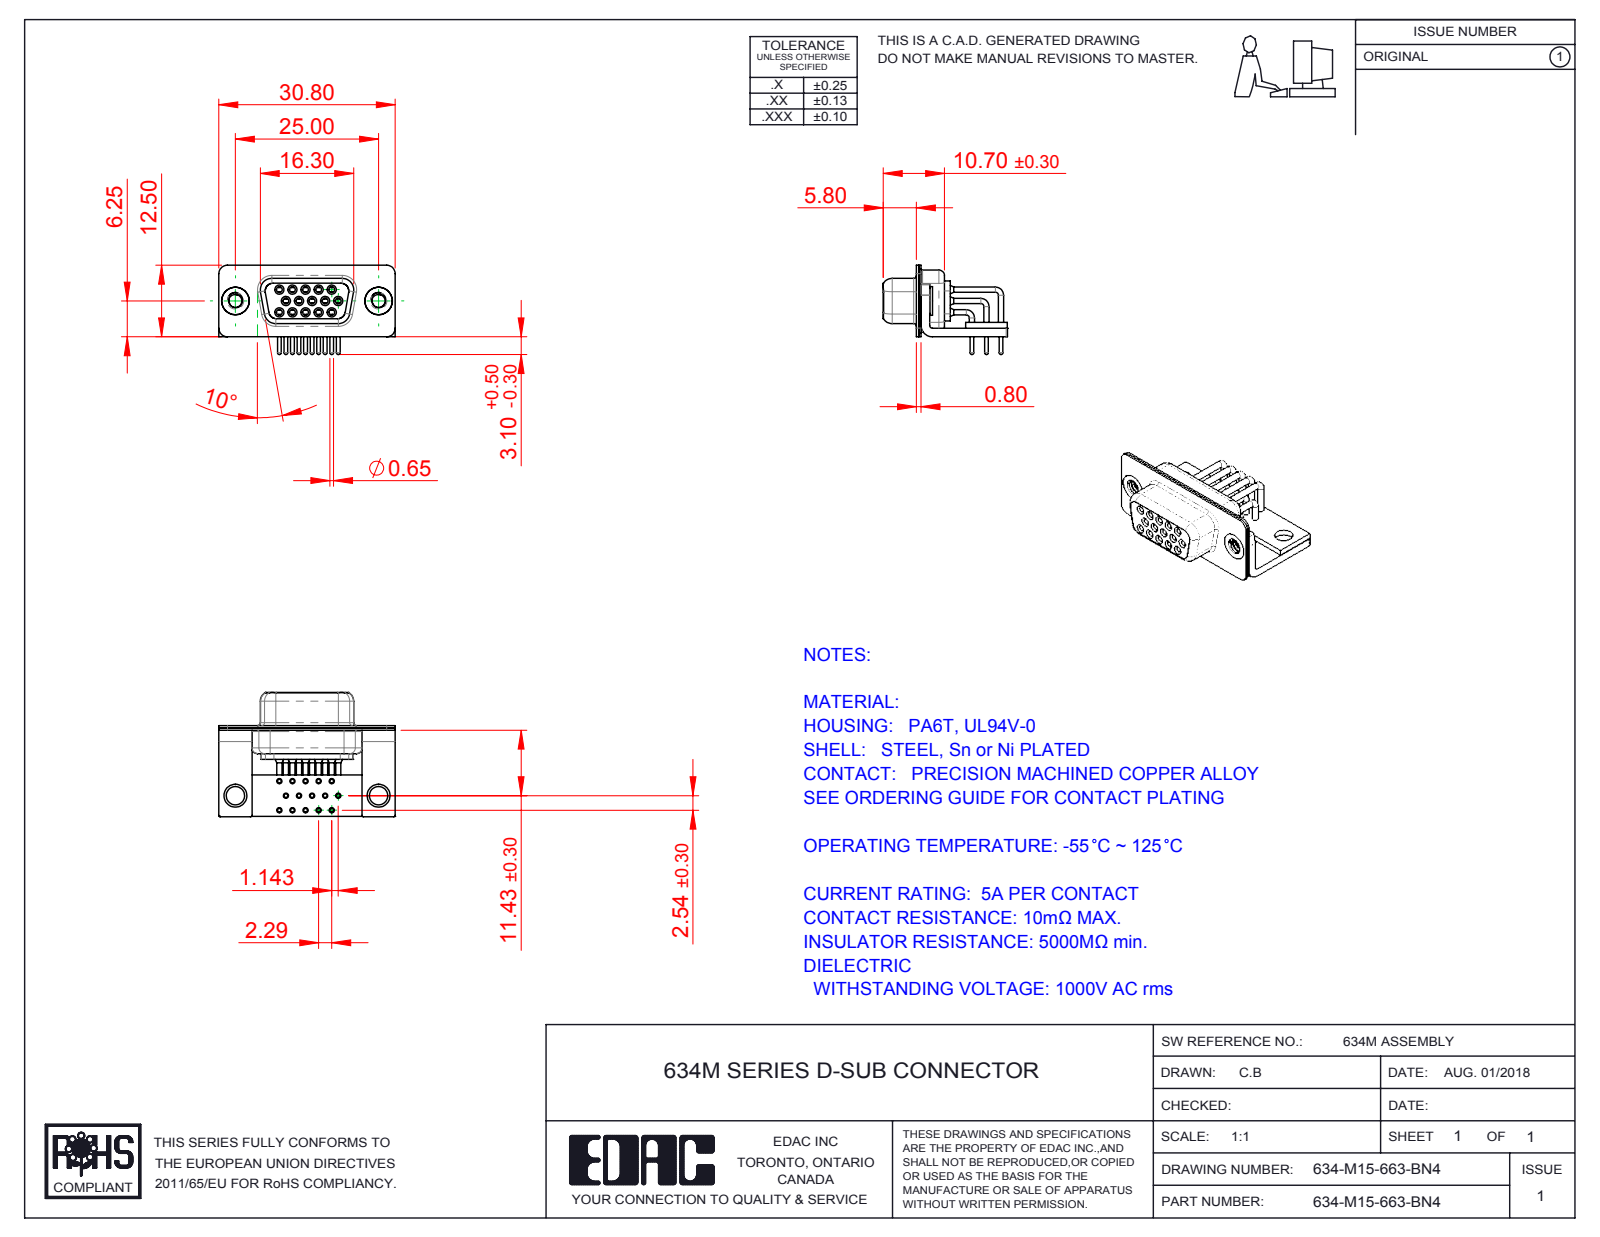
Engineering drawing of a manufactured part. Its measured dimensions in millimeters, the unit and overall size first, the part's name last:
Units: millimetres
Overall size (bounding box): 30.8 × 21.7 × 15.6
Round holes (diameter × count): ⌀0.9 ×15, ⌀1 ×15, ⌀1.1 ×15, ⌀1.7 ×15, ⌀1.8 ×15, ⌀2 ×15, ⌀2.26 ×2, ⌀3.2 ×2, ⌀4 ×2, ⌀4.8 ×2
Round bosses / shafts (diameter × count): ⌀1.6 ×15, ⌀1.5 ×15, ⌀0.9 ×15, ⌀0.65 ×15, ⌀5 ×2, ⌀4.9 ×2, ⌀2 ×1
Partial cylindrical surfaces — rounded edges, fillets, slot ends (radius × count): R0.25 ×16, R1.5 ×16, R2 ×13, R1.35 ×8, R1.6 ×8, R0.5 ×5, R0.6 ×4, R0.65 ×4
Main face-to-face distances: 0.4, 0.8, 1.5, 1, 2.3, 1.9, 9.35, 2.5, 1.45, 0.85
Hole centre spacings: 2.29, 2.28, 4.57, 3.96, 4.27, 2.78, 6.05, 6.86
Volume: 2 216 mm³ · Surface area: 6 817 mm²
Bodies: 23 solids, 1154 faces (318 planar, 534 cylindrical, 302 other)
Part name (STEP PRODUCT): 634M Contact Row 3; 634M Stabilizer Board_15 Contacts; 634M Contact Row 2; 634M Contact Row 1 (+6 more)
STEP written by: SolidWorks 2016 (CONFIG_CONTROL_DESIGN)
